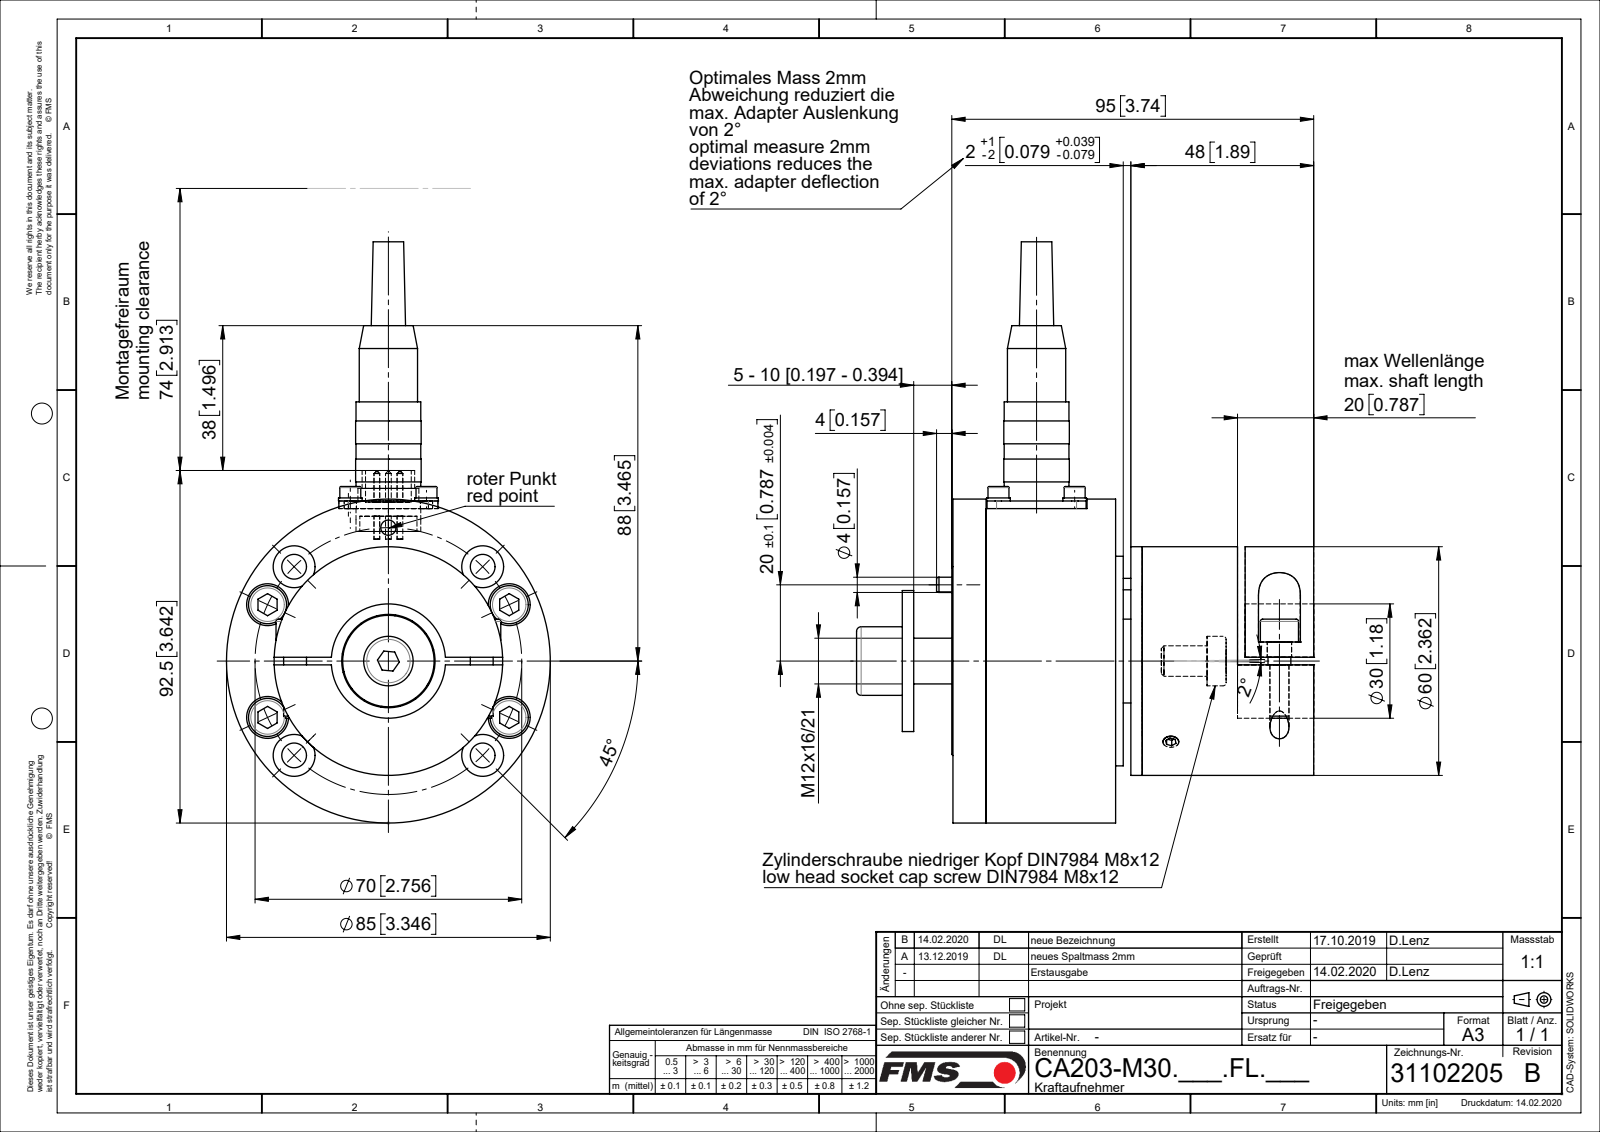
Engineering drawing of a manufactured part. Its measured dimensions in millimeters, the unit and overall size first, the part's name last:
Units: millimetres
Overall size (bounding box): 152.5 × 120.5 × 85
Round holes (diameter × count): ⌀2.6 ×8, ⌀6.5 ×8, ⌀11 ×8, ⌀5.15 ×6, ⌀3.2 ×4, ⌀3.6 ×4, ⌀4 ×4, ⌀7 ×4, ⌀6.4 ×2, ⌀3 ×1, ⌀4.33 ×1, ⌀7.15 ×1
Round bosses / shafts (diameter × count): ⌀6 ×10, ⌀3 ×8, ⌀10 ×6, ⌀1.5 ×5, ⌀6.2 ×4, ⌀5.5 ×4, ⌀5 ×4, ⌀85 ×1
Partial cylindrical surfaces — rounded edges, fillets, slot ends (radius × count): R2.5 ×4, R5 ×2, R5.5 ×2
Main face-to-face distances: 45, 49.5, 2, 9, 11.5, 31.5, 43, 10, 1.5, 40.5
Hole centre spacings: 20, 24.78, 25.2, 32.8, 35, 51.14, 56.46, 28.28
Volume: 317 154 mm³ · Surface area: 110 424 mm²
Bodies: 37 solids, 671 faces (221 planar, 310 cylindrical, 140 other)
Part name (STEP PRODUCT): C0709101_DM30; C0709081; C0612056; C0709072 (+8 more)
STEP written by: Mechanical Desktop 2009 (CONFIG_CONTROL_DESIGN)
